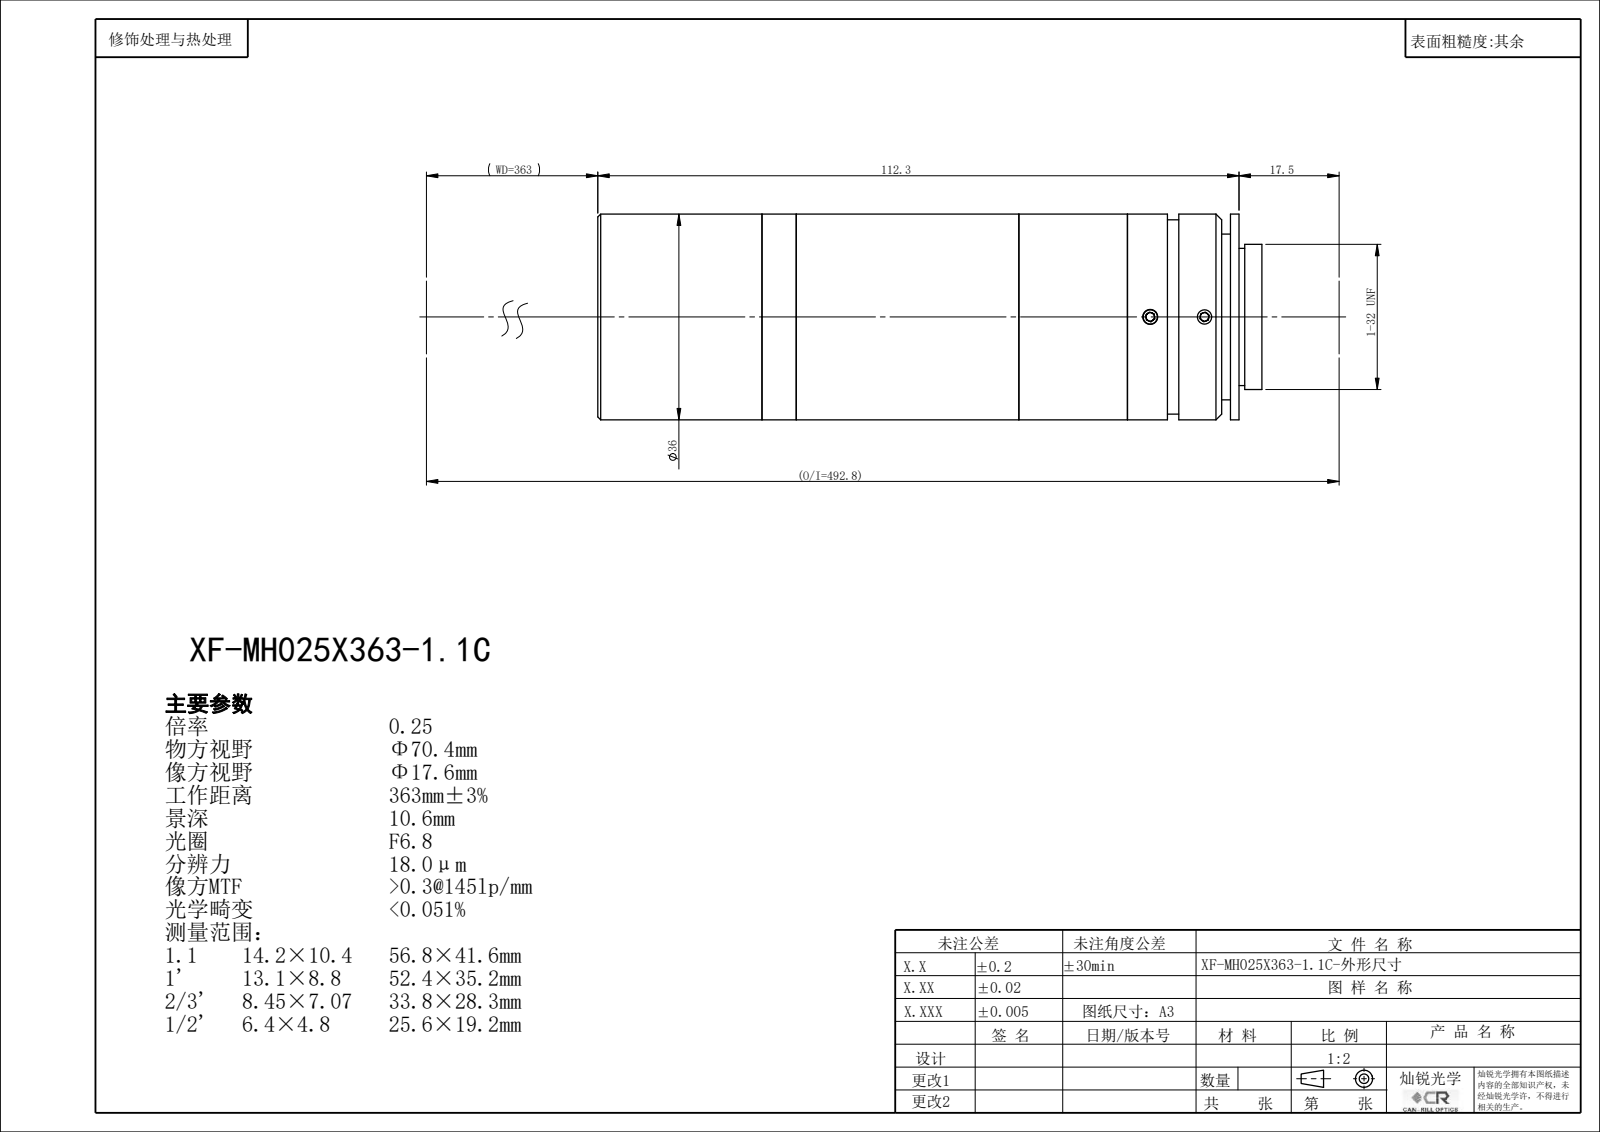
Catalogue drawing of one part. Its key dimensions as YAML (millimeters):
part_name: "XF-MH025X363-1.1C"
step_written_by: "SolidWorks 2022 (CONFIG_CONTROL_DESIGN)"
units: millimeters
bodies: {solids: 0, faces: 132, planar: 70, cylindrical: 40, other: 22}
overall_size: [116.25, 36, 36]
round_holes:
  - {diameter: 2.5, count: 3}
  - {diameter: 22.4, count: 1}
  - {diameter: 24, count: 1}
  - {diameter: 26, count: 1}
  - {diameter: 26.4, count: 1}
  - {diameter: 29.4, count: 1}
  - {diameter: 33.4, count: 1}
  - {diameter: 34.5, count: 1}
round_bosses_or_shafts:
  - {diameter: 36, count: 1}
  - {diameter: 34, count: 1}
  - {diameter: 25.4, count: 1}
face_to_face_distances: [19.53, 1.5, 18.03, 19, 37.03, 38.53, 69.28, 88.28, 106.31, 107.81]
